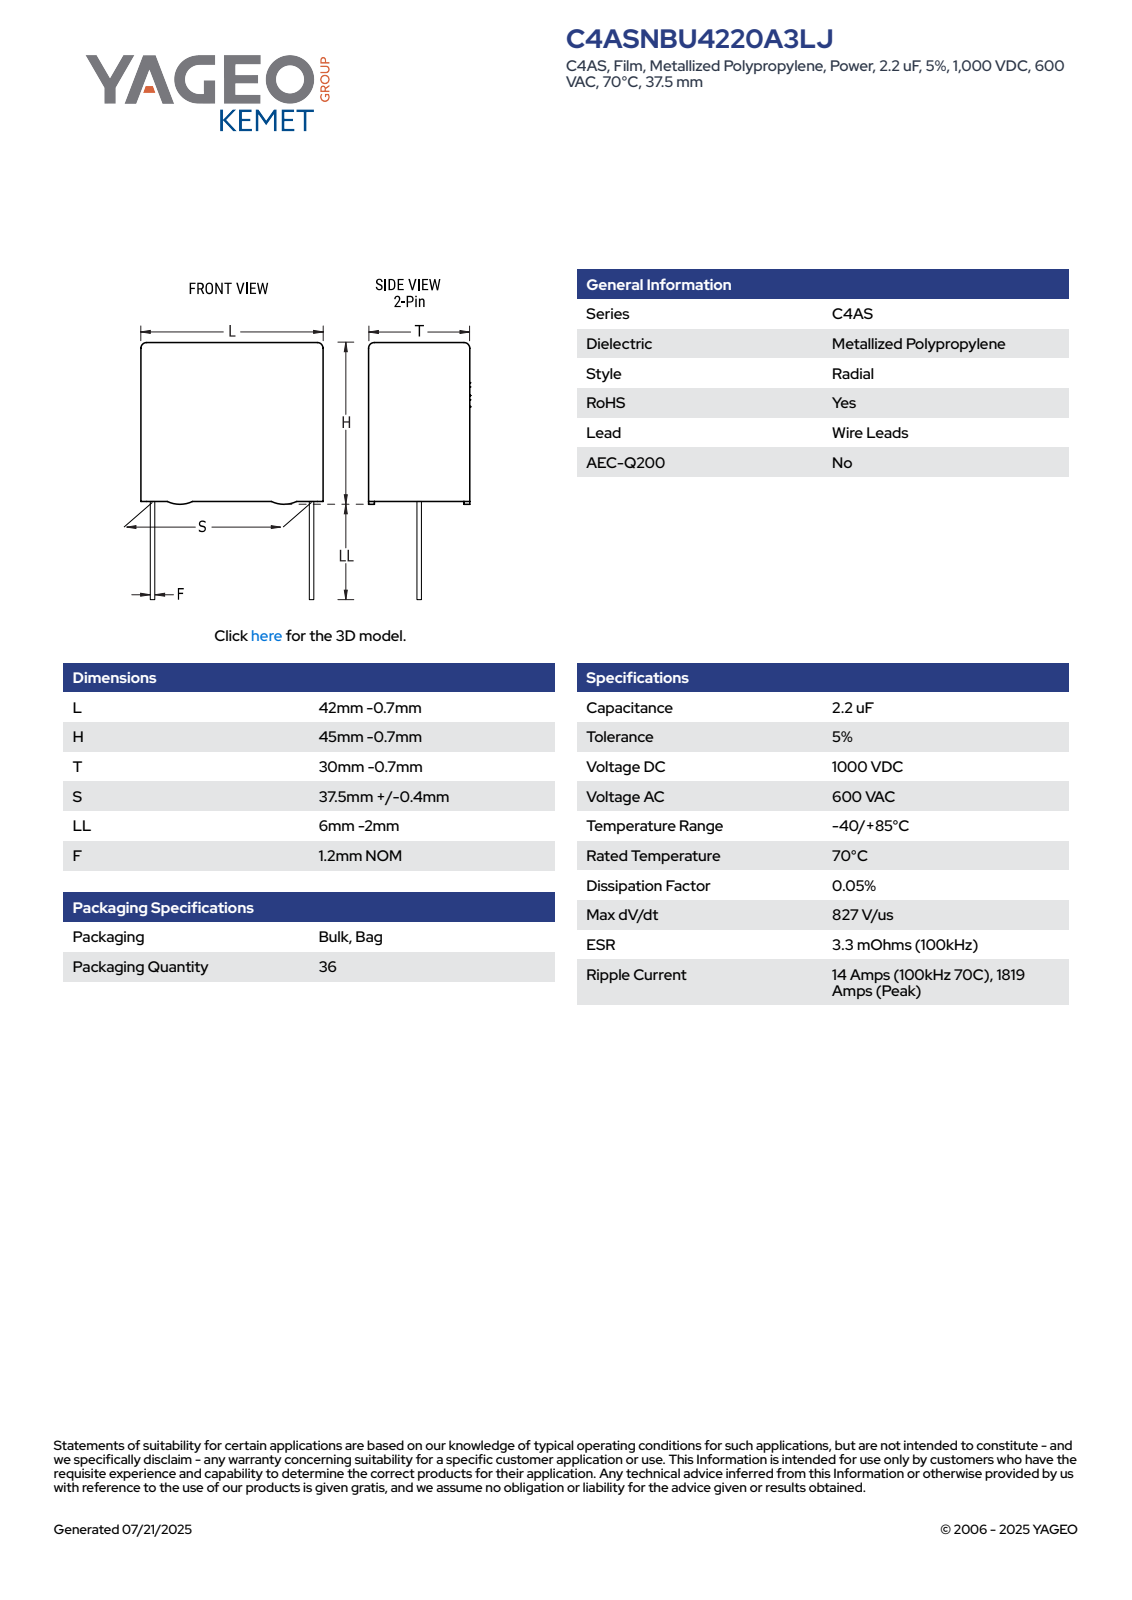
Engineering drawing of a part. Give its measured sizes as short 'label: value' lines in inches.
name: CFP_RB_42X45X30_L41.3H44.3T29.3S37.5LL4F1.2
written by: SolidWorks 2014 (AUTOMOTIVE_DESIGN)
unit: in
bodies: 4 solids, 89 faces (81 planar, 8 cylindrical, 0 other)
size: 1.902 × 1.626 × 1.154
volume: 3.208 in³; area: 13.46 in²
bosses: 2× ⌀0.047
rounds: 4× R0.02
face distances: 1.154, 1.626, 1.709, 0.035, 1.744, 0.066, 1.088, 1.022, 1.138, 0.157
